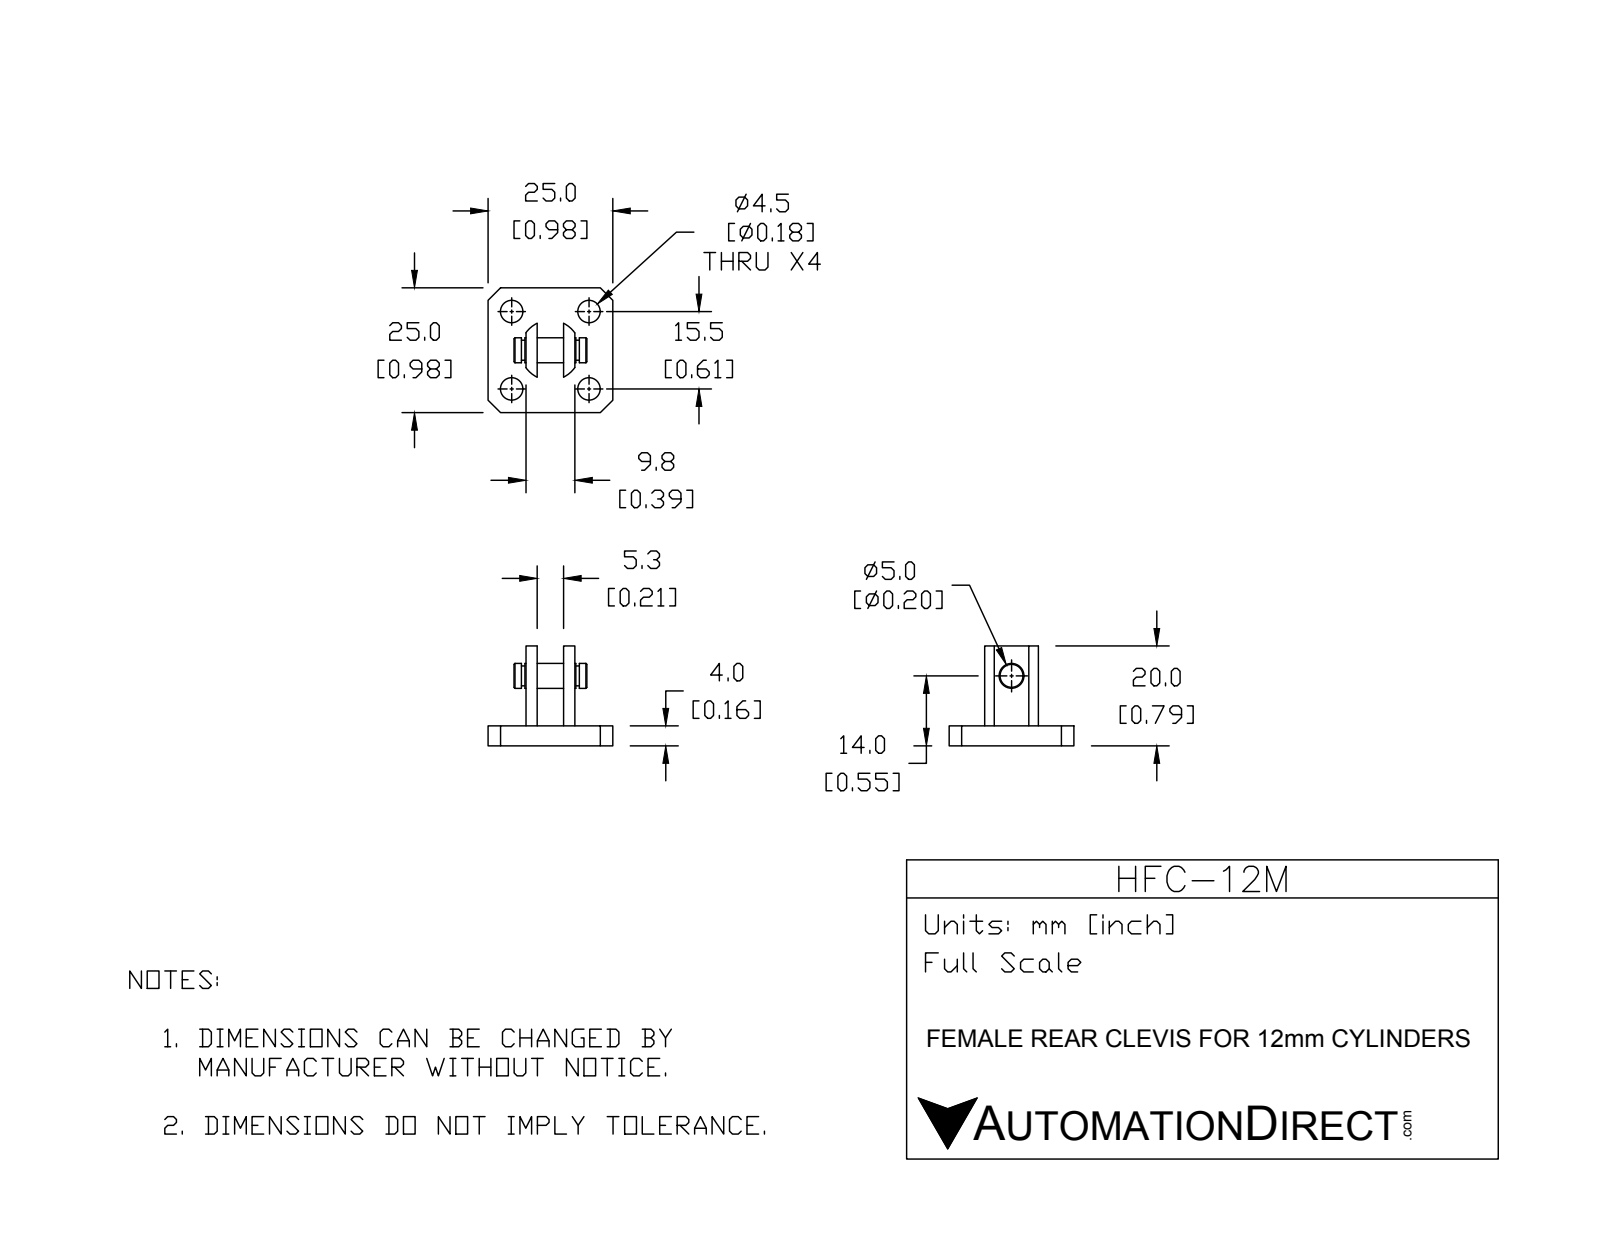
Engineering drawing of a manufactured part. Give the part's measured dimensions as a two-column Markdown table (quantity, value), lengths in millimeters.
| quantity | value |
| --- | --- |
| part name | HFC-12M |
| STEP written by | SolidWorks 2015 (CONFIG_CONTROL_DESIGN) |
| units | millimeters |
| bodies | 2 solids, 56 faces (22 planar, 26 cylindrical, 8 other) |
| overall size | 25 × 25 × 20 |
| volume | 3 043 mm³ |
| surface area | 2 735 mm² |
| round holes (diameter × count) | 4.5 × 4 |
| round bosses / shafts (diameter × count) | 5 × 1, 4 × 1 |
| partial cylindrical surfaces (radius × count) | 6 × 1 |
| main face-to-face distances | 4, 2.25, 7.55, 7.6, 9.85, 15.15, 17.4, 25, 5.3, 9.8 |
| hole center spacings | 15.5, 21.92 |
